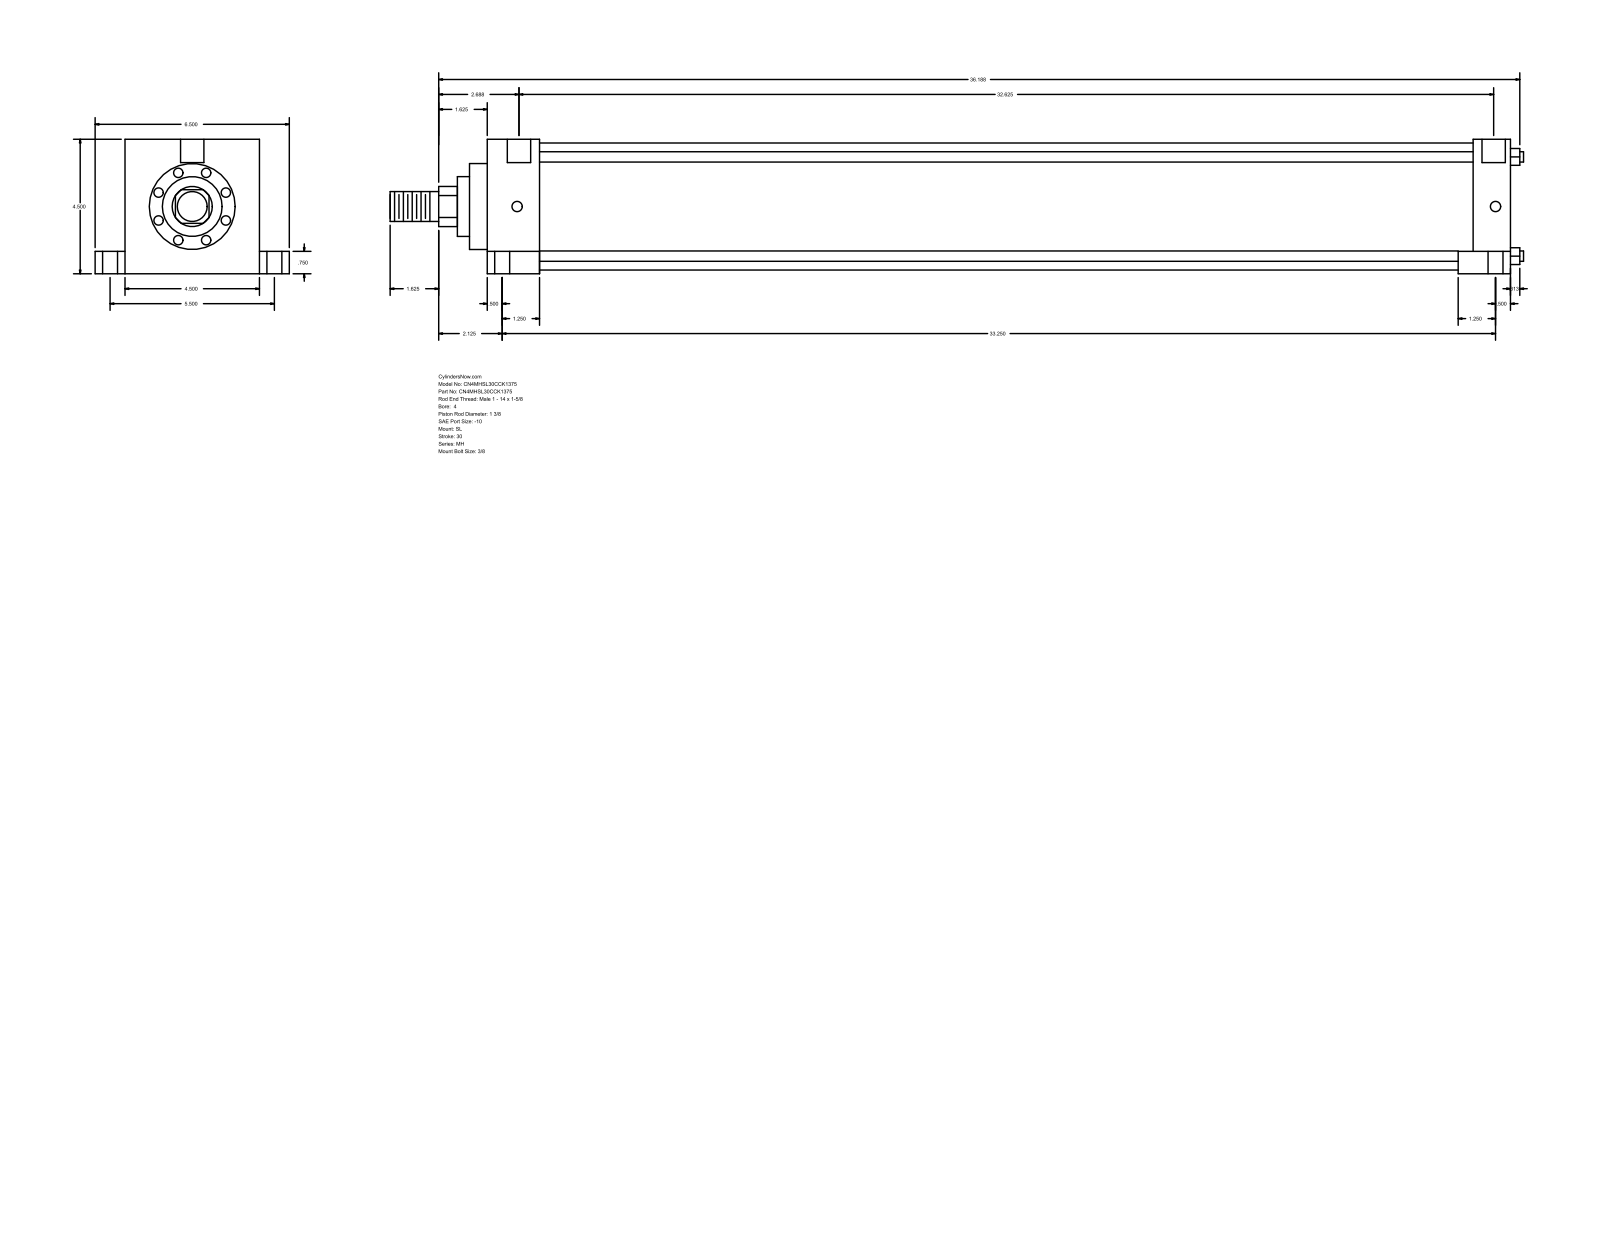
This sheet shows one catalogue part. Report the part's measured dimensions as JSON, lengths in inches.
{"part_name": "MH_SL__0400_1.375", "step_written_by": "GSSL Pune (CONFIG_CONTROL_DESIGN)", "units": "inches", "bodies": {"solids": 0, "faces": 110, "planar": 77, "cylindrical": 33, "other": 0}, "overall_size": [37.937, 6.5, 4.5], "round_holes": [[0.344, 4], [0.5, 4], [0.75, 4], [0.781, 2]], "round_bosses_or_shafts": [[0.345, 4], [4.25, 1], [2.875, 1], [2, 1], [1.375, 1], [1, 1]], "partial_cylinders_radius": [[0.672, 1]], "face_to_face_distances": [4.5, 34.25, 1.75, 32.5, 33, 31.25, 1.25, 1, 5.5, 0.75], "hole_center_spacings": [2.75, 2.751, 2.795, 2.807, 5.5, 32.75, 32.803, 32.865]}
